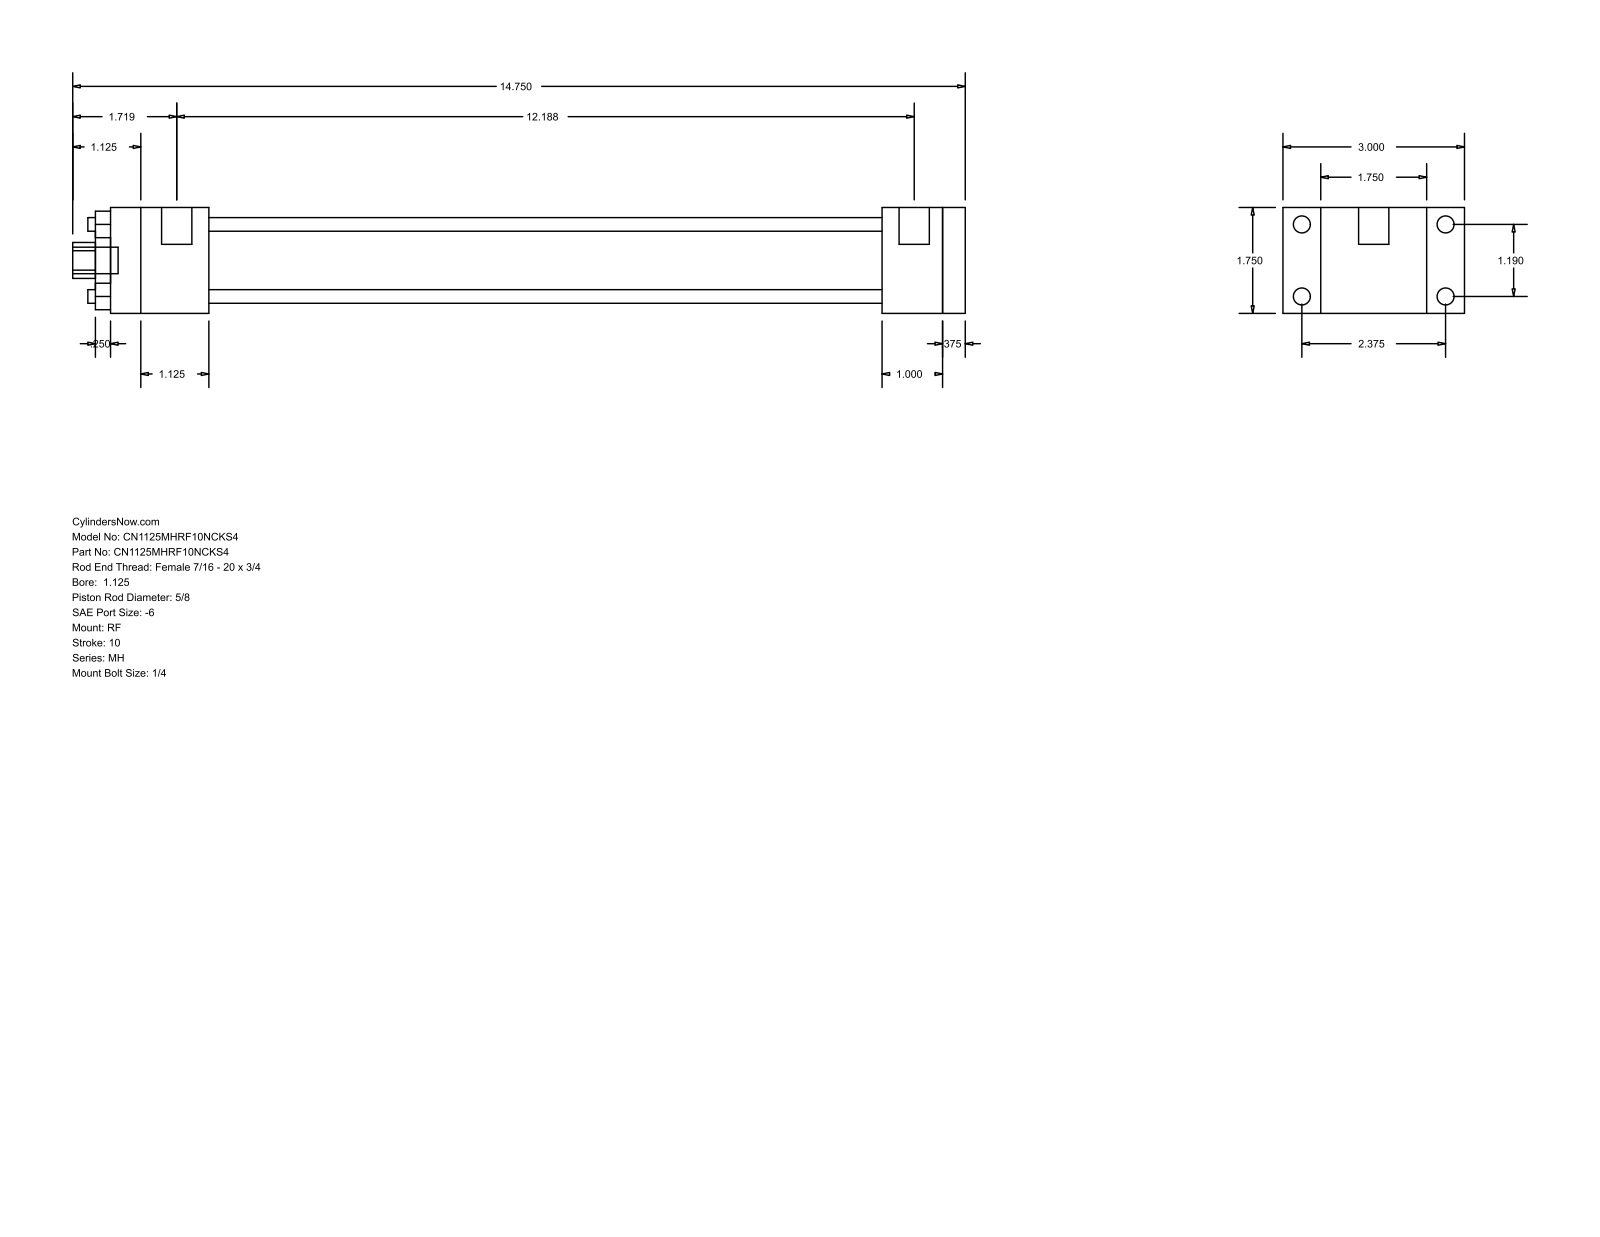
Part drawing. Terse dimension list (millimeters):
name: MH_RF__0112_0.625
written by: GSSL Pune (CONFIG_CONTROL_DESIGN)
unit: mm
bodies: 0 solids, 92 faces (64 planar, 28 cylindrical, 0 other)
size: 374.65 × 76.2 × 44.45
holes: 4× ⌀5.71, 1× ⌀15.88, 1× ⌀28.57, 1× ⌀34.92
bosses: 4× ⌀7.14, 4× ⌀5.56, 2× ⌀12.7, 1× ⌀11.11
rounds: 1× R7.54
face distances: 44.46, 9.53, 358.77, 15.87, 307.97, 317.5, 282.58, 25.39, 34.92, 41.27
hole spacings: 21.37, 30.22, 42.74
